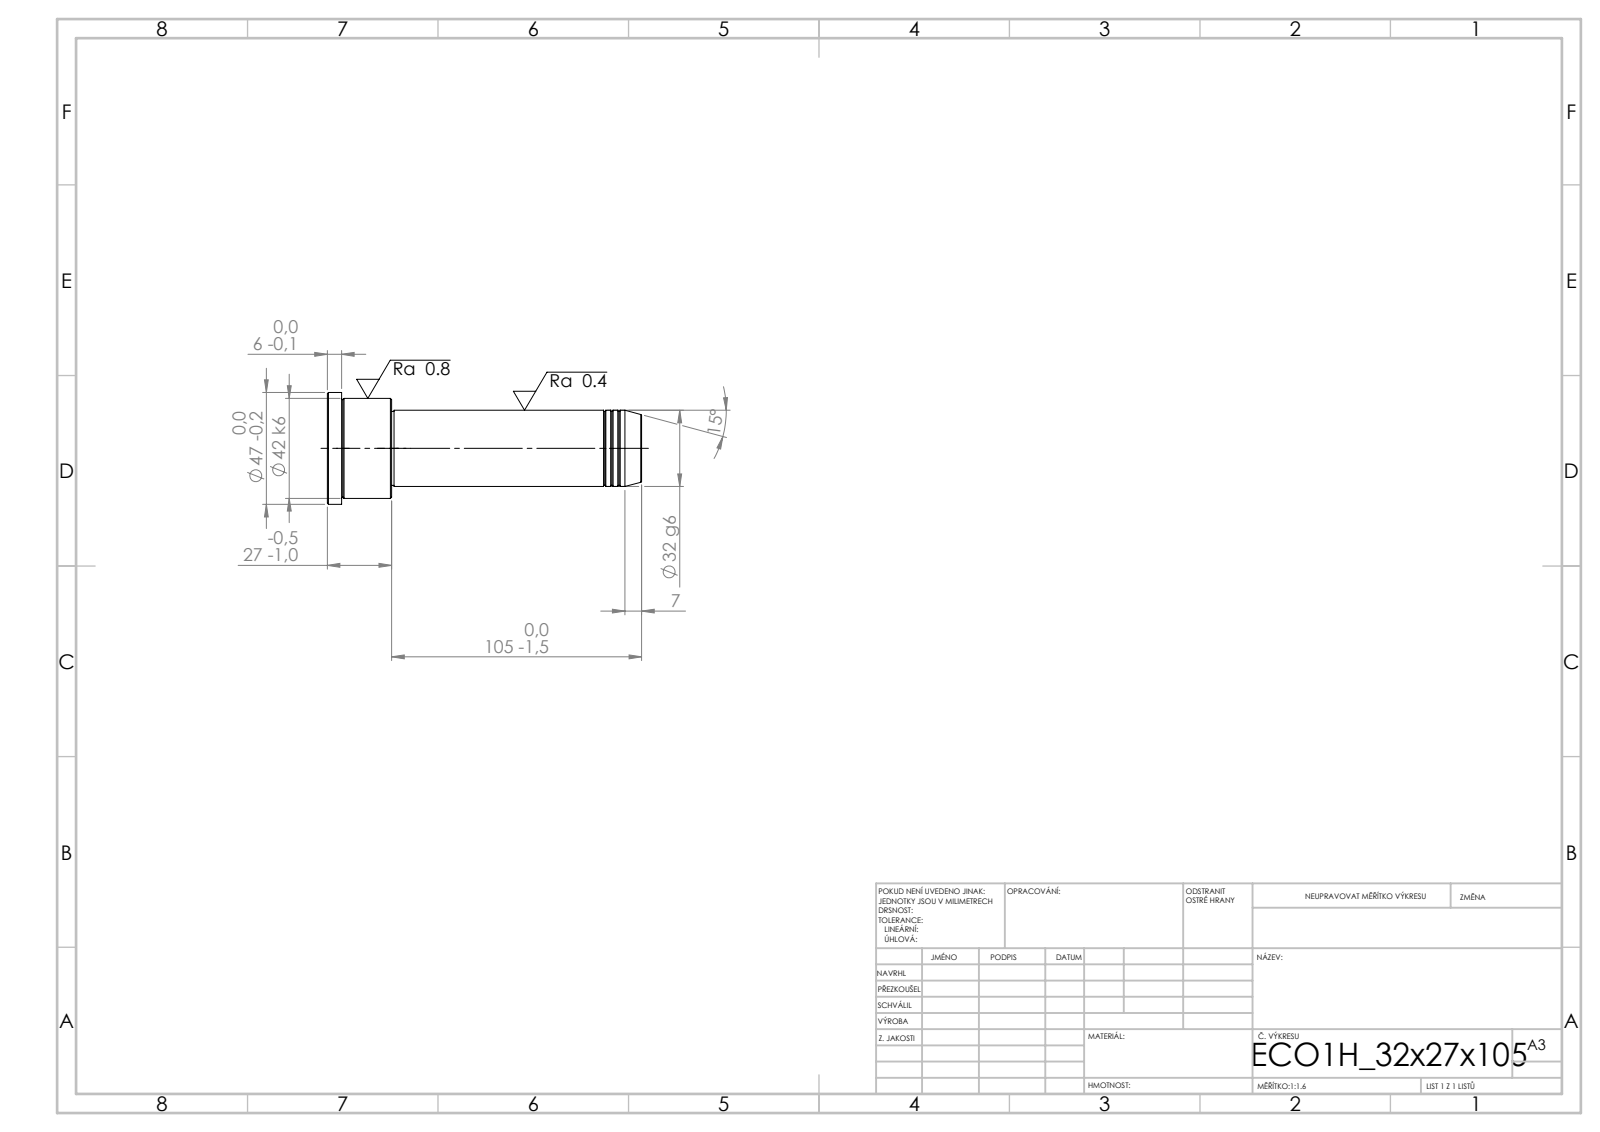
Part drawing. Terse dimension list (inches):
written by: SolidWorks 2019 (CONFIG_CONTROL_DESIGN)
unit: in
bodies: 1 solid, 43 faces (5 planar, 14 cylindrical, 24 other)
size: 5.197 × 1.85 × 1.85
volume: 7.51 in³; area: 27.47 in²
bosses: 1× ⌀1.85, 1× ⌀1.654, 1× ⌀1.26, 1× ⌀1.22
face distances: 5.197, 4.134, 1.063, 4.961, 0.827, 0.236, 4.094, 0.039, 0.866, 1.102
